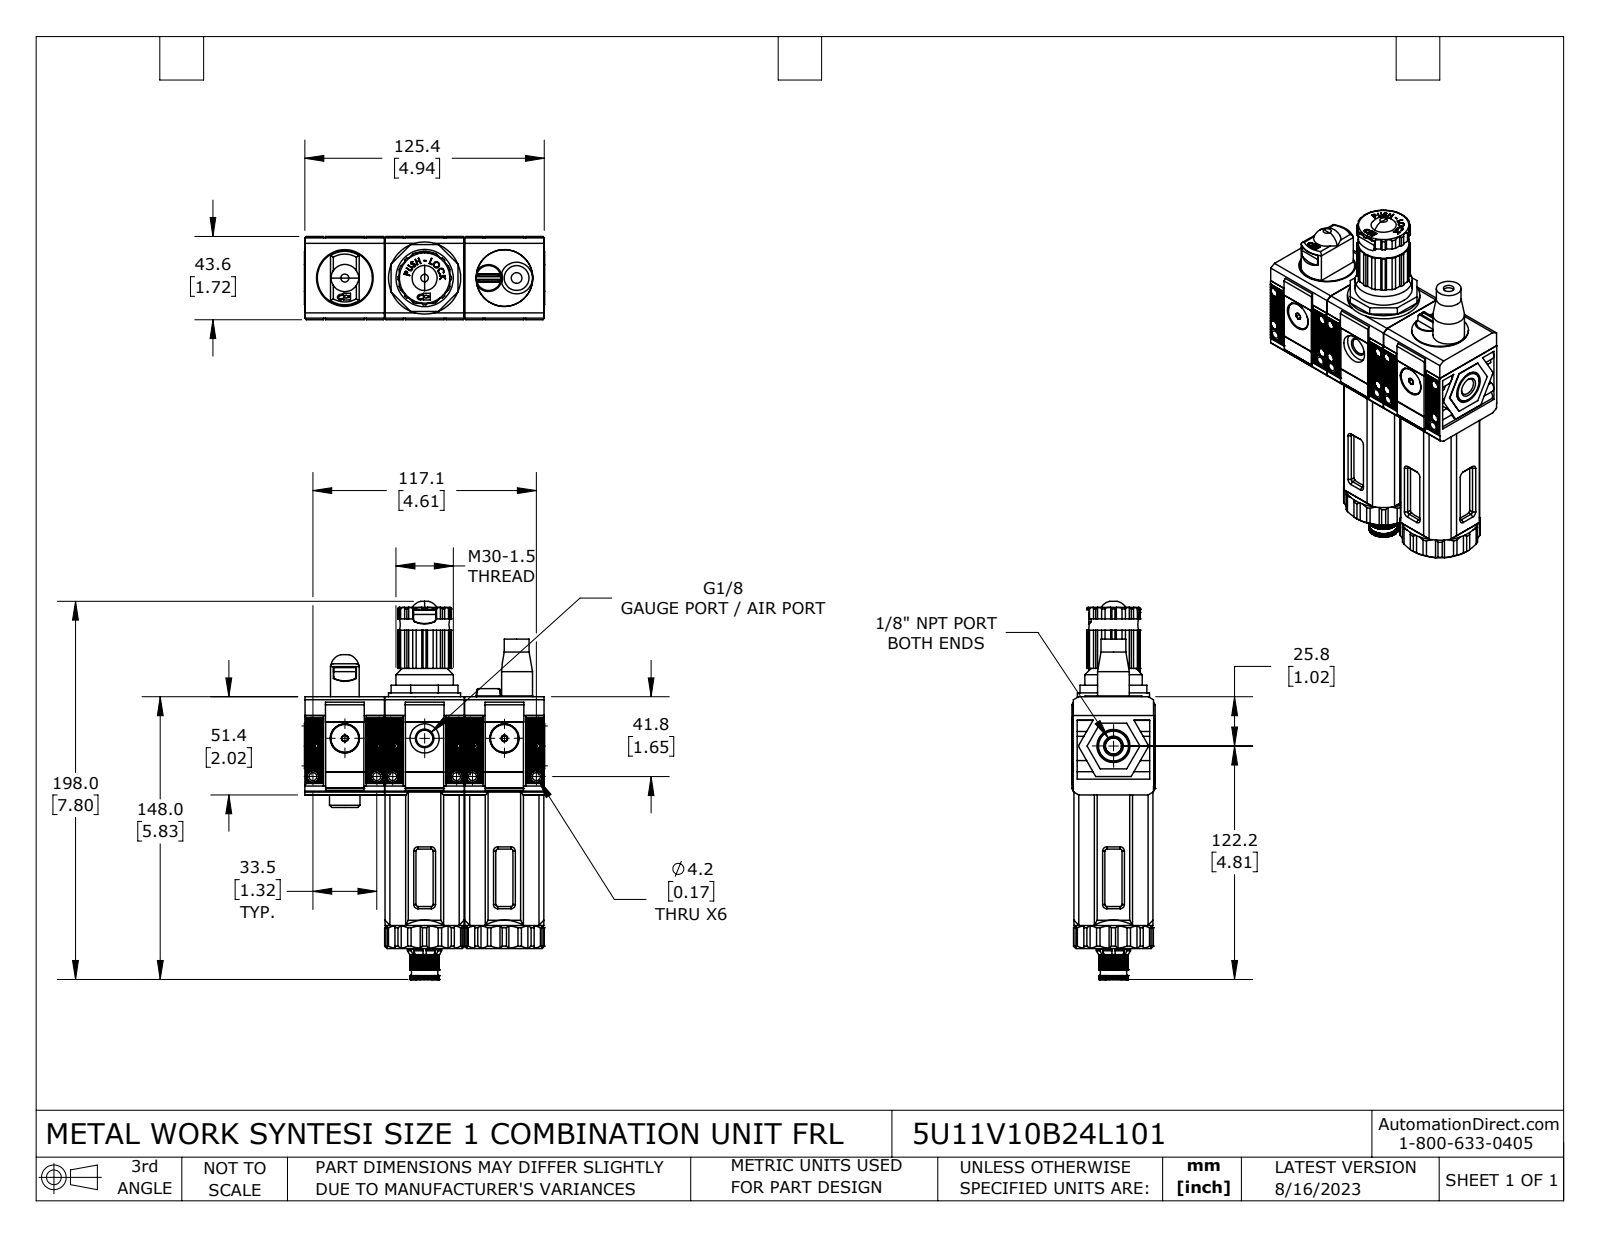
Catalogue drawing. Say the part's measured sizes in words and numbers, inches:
The part is named "5U11V10B24L101". Its 3-D file was written by "SolidWorks 2021 (CONFIG_CONTROL_DESIGN)". It is 40 solids with 4635 faces: 3330 planar, 890 cylindrical and 415 other. Overall it measures 7.795 by 4.953 by 1.717 inches. Its volume is 23.77 cubic inches and its surface area 267.6 square inches. Round holes: 12 of diameter 0.083, 12 of diameter 0.118, 12 of diameter 0.185, 6 of diameter 0.165, 4 of diameter 0.337, 3 of diameter 0.602, 2 of diameter 0.138, 2 of diameter 1.169, 2 of diameter 1.181, 2 of diameter 1.232, 2 of diameter 1.339, 2 of diameter 1.394. Round bosses or shafts: 12 of diameter 0.181, 12 of diameter 0.102, 6 of diameter 0.244, 3 of diameter 0.591, 3 of diameter 0.383, 2 of diameter 1.63, 2 of diameter 1.402, 2 of diameter 0.984. Partial cylindrical surfaces (rounded edges, fillets, slot ends): 14 of radius 0.039, 12 of radius 0.122, 7 of radius 0.059, 4 of radius 0.024, 2 of radius 0.008, 2 of radius 0.018, 2 of radius 0.033, 2 of radius 0.051. The main face-to-face distances are 1.646, 1.638, 1.642, 0.043, 1.673, 1.63, 1.339, 0.307, 3.291, 1.654. The hole center spacings are 1.646, 1.84, 3.291, 0.222, 0.742, 0.823, 0.9, 1.027.
